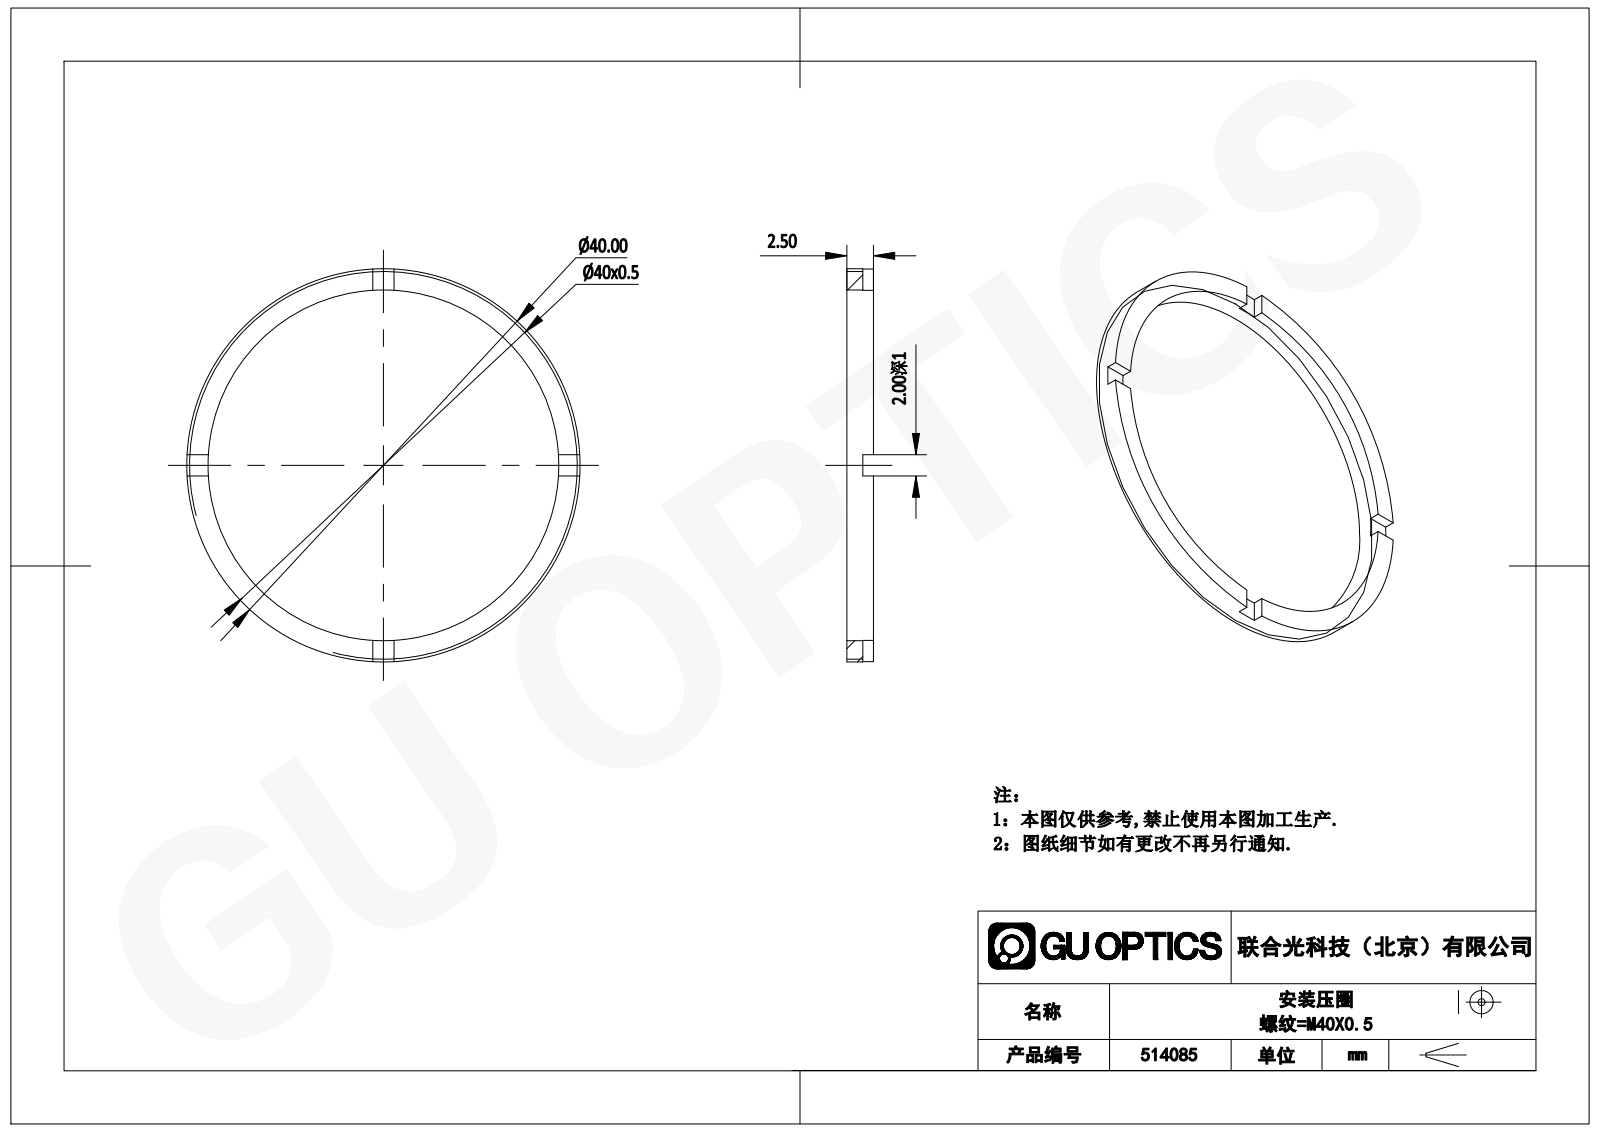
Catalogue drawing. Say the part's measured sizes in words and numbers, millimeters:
The part is named "514085". Its 3-D file was written by "SolidWorks 2020 (CONFIG_CONTROL_DESIGN)". It is 1 solid with 21 faces: 17 planar, 4 cylindrical and 0 other. Overall it measures 40 by 40 by 2.5 millimeters. Its volume is 581 cubic millimeters and its surface area 1 074 square millimeters. Round holes: 1 of diameter 36. Round bosses or shafts: 1 of diameter 40. The main face-to-face distances are 2.5, 1.5, 1, 2.
